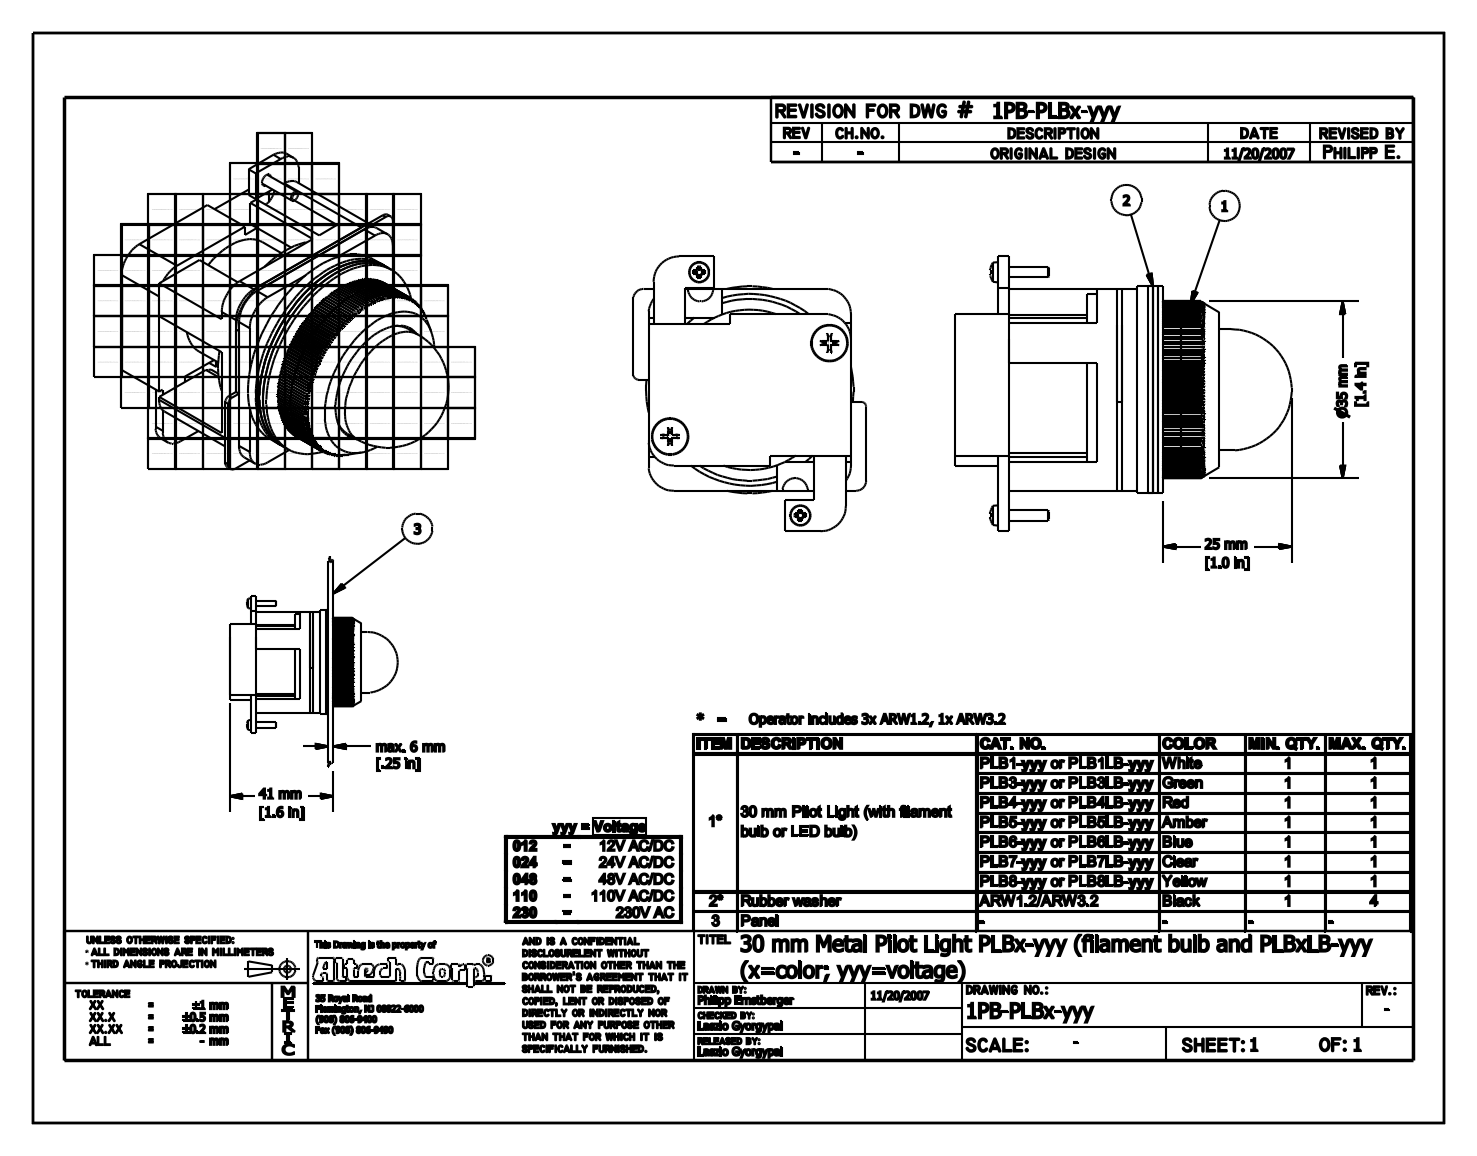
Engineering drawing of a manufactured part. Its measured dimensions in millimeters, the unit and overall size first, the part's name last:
Units: millimetres
Overall size (bounding box): 66.43 × 54.41 × 46
Round holes (diameter × count): ⌀2.5 ×2, ⌀3.5 ×2, ⌀22 ×1, ⌀24.5 ×1, ⌀24.6 ×1, ⌀25.75 ×1, ⌀26 ×1, ⌀30 ×1, ⌀30.5 ×1, ⌀31 ×1, ⌀31.75 ×1
Round bosses / shafts (diameter × count): ⌀3.18 ×2, ⌀2 ×2, ⌀1.8 ×2, ⌀41 ×1, ⌀28 ×1, ⌀25 ×1, ⌀24 ×1
Partial cylindrical surfaces — rounded edges, fillets, slot ends (radius × count): R5 ×8, R1 ×2, R2 ×2, R2.5 ×2, R7.23 ×1, R13.7 ×1, R13.75 ×1, R17.5 ×1
Main face-to-face distances: 1, 3, 7, 2, 40, 0.85, 6.15, 10.5, 30.5, 3.85
Hole centre spacings: 18.27, 25.35, 26.81, 29.33, 30.12, 33.04, 34.6, 36.53
Volume: 43 680 mm³ · Surface area: 34 801 mm²
Bodies: 15 solids, 1771 faces (885 planar, 436 cylindrical, 450 other)
Part name (STEP PRODUCT): PLBx-xxx; bronze_base; gasket; plastic_standoff (+8 more)
STEP written by: Autodesk Inventor 2008 (AUTOMOTIVE_DESIGN)
